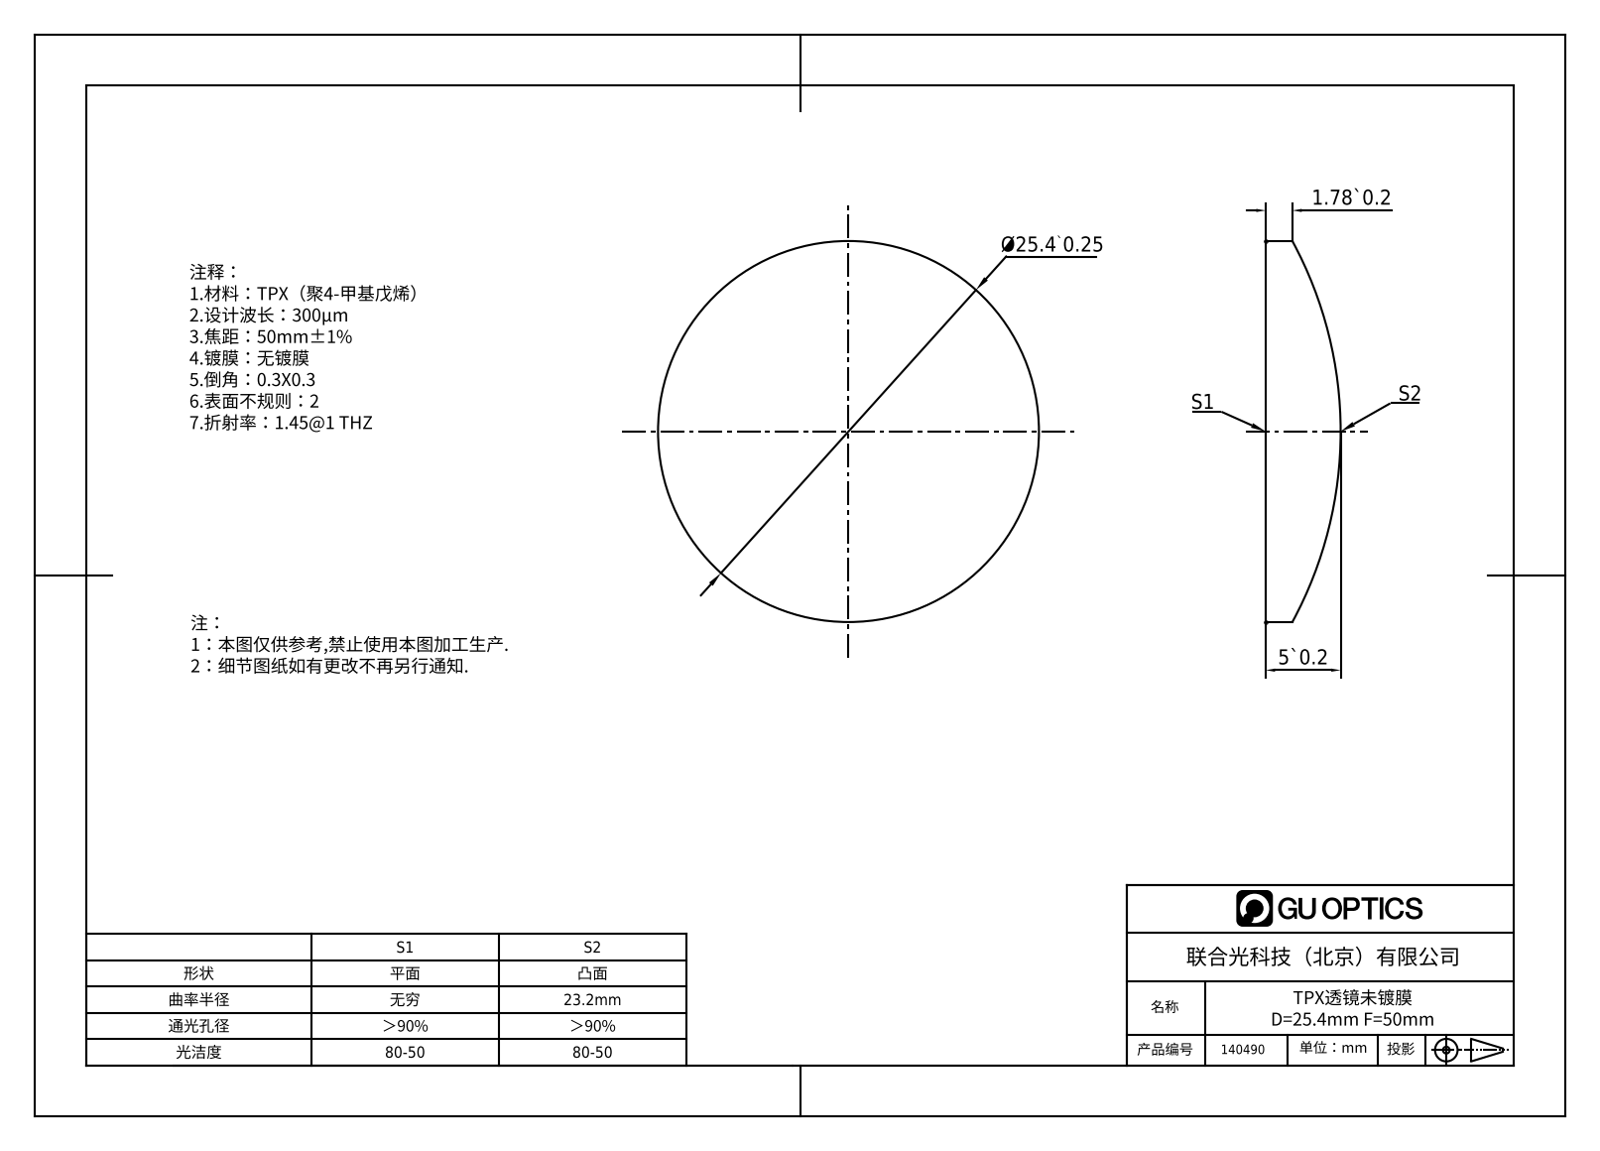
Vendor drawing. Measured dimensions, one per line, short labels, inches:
name: 140490建模
written by: SolidWorks 2020 (AUTOMOTIVE_DESIGN)
unit: in
bodies: 1 solid, 5 faces (1 planar, 2 cylindrical, 2 other)
size: 2 × 2 × 0.394
volume: 0.847 in³; area: 7.366 in²
bosses: 1× ⌀2
